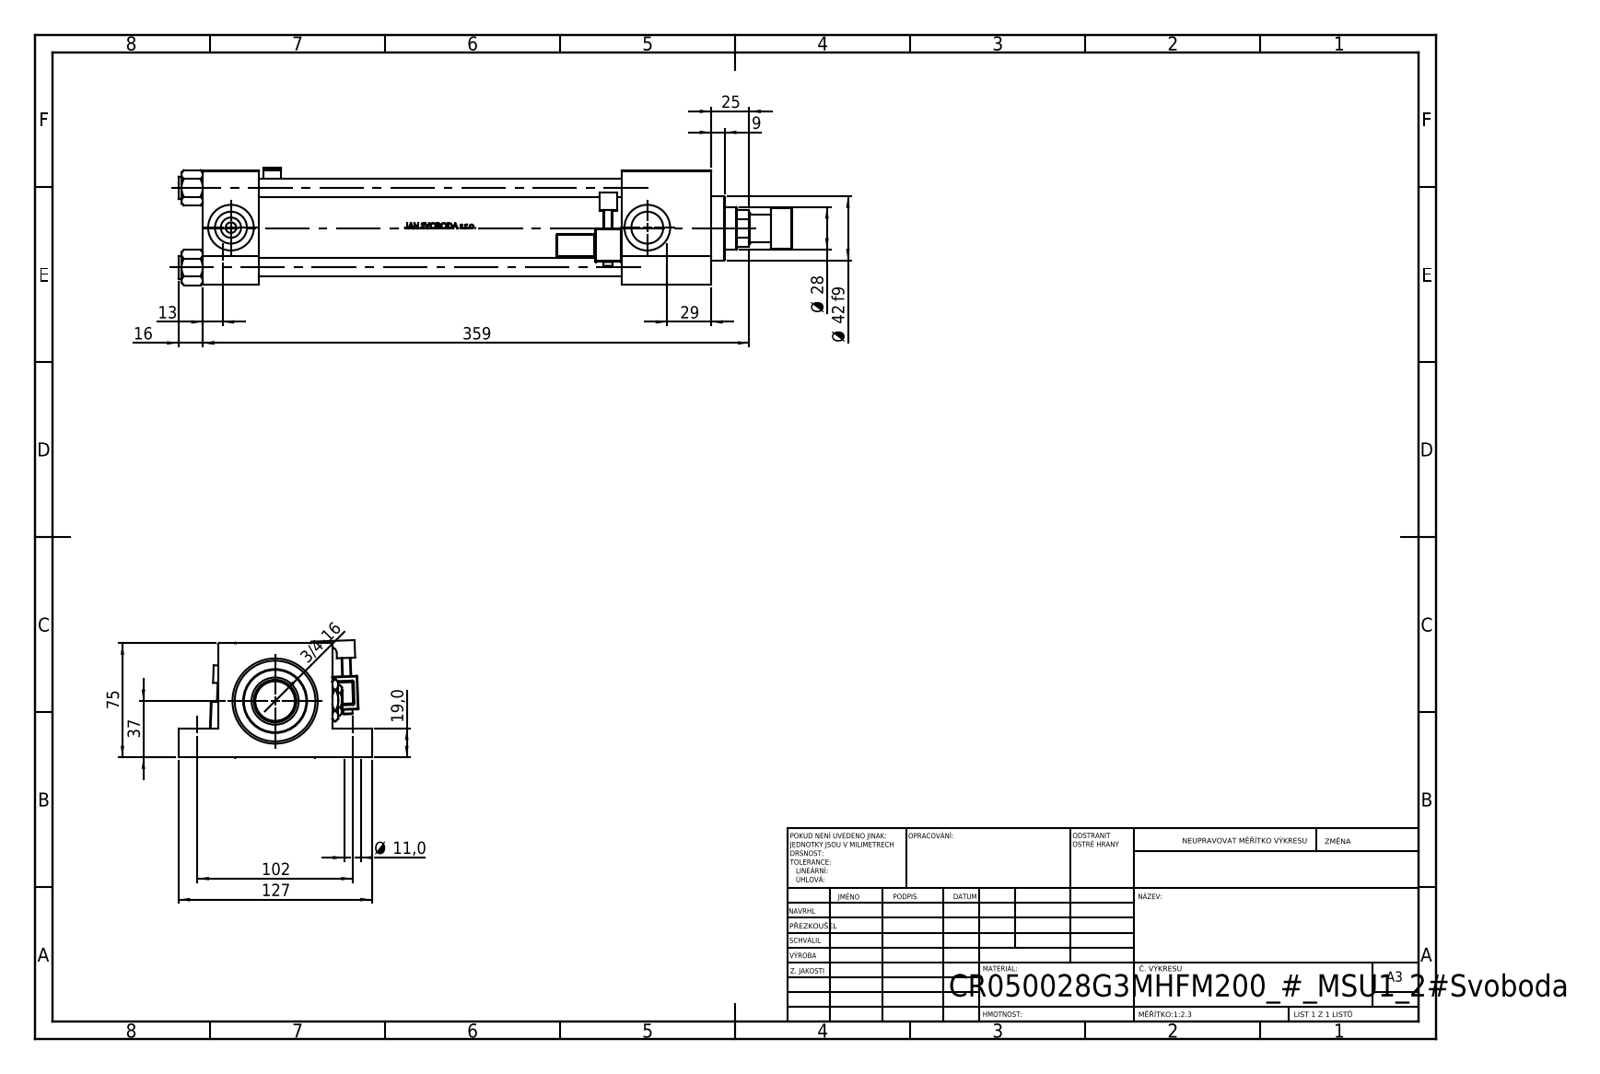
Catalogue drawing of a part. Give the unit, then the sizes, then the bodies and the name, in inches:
Units: inches
Overall size (bounding box): 15.866 × 5 × 3.043
Round holes (diameter × count): ⌀0.433 ×4, ⌀0.472 ×4, ⌀0.276 ×2, ⌀0.825 ×2, ⌀1.181 ×2, ⌀0.728 ×1, ⌀1.102 ×1, ⌀1.22 ×1, ⌀1.614 ×1, ⌀1.969 ×1, ⌀2.087 ×1
Round bosses / shafts (diameter × count): ⌀0.591 ×4, ⌀0.236 ×2, ⌀2.205 ×1, ⌀1.654 ×1, ⌀1.063 ×1, ⌀0.709 ×1
Partial cylindrical surfaces — rounded edges, fillets, slot ends (radius × count): R0.02 ×48, R0.039 ×2, R0.098 ×2, R0.157 ×2, R0.236 ×1
Main face-to-face distances: 2.953, 1.457, 13.15, 11.693, 2.205, 0.748, 10.827, 9.37, 2.323, 1.024
Hole centre spacings: 2.059, 1.442, 1.47, 2.912, 4.016, 11.496, 12.177, 10.768
Volume: 66.94 in³ · Surface area: 443.3 in²
Bodies: 16 solids, 1351 faces (539 planar, 196 cylindrical, 616 other)
Part name (STEP PRODUCT): V215_VC_A; V215CR_G_Body; NUT_M5_G; V215CR_G_TYCINKA (+4 more)
STEP written by: SolidWorks 2019 (CONFIG_CONTROL_DESIGN)
